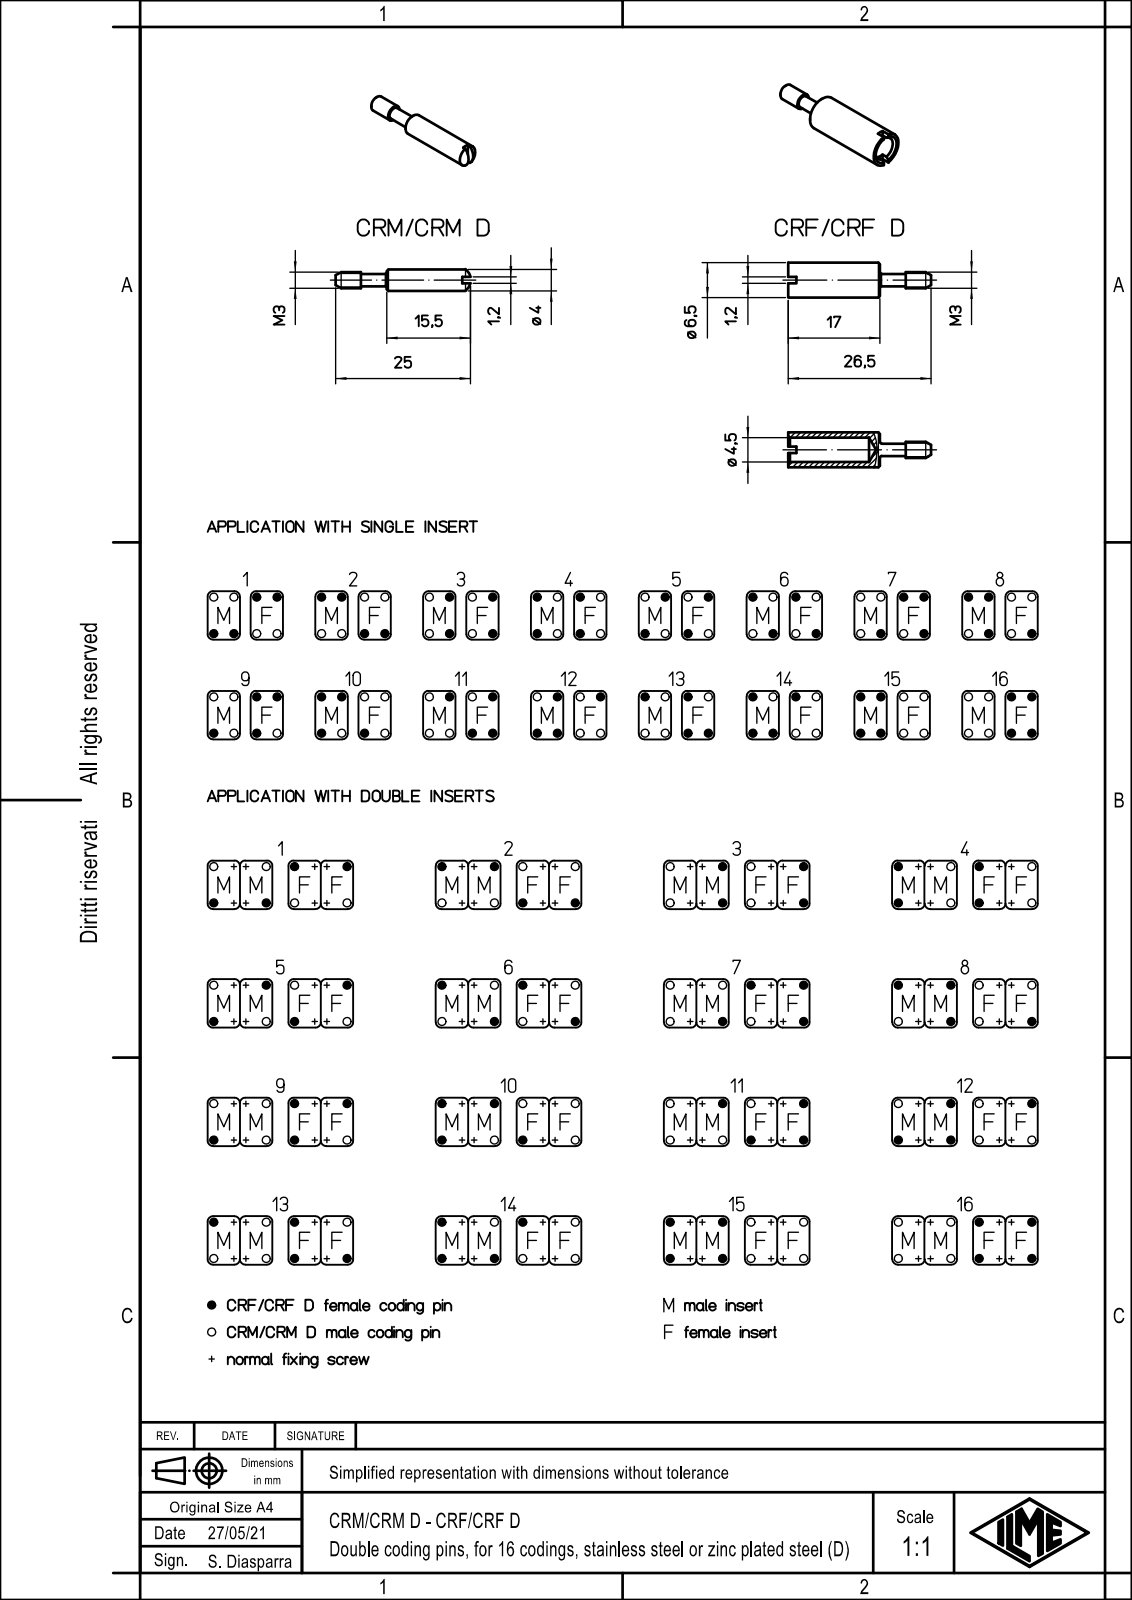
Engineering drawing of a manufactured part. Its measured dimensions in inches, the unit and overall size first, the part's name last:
Units: inches
Overall size (bounding box): 1.024 × 0.256 × 0.256
Round holes (diameter × count): ⌀0.177 ×1
Round bosses / shafts (diameter × count): ⌀0.256 ×1, ⌀0.118 ×1, ⌀0.098 ×1
Main face-to-face distances: 0.157, 0.512, 0.669, 0.354, 1.024, 0.031, 0.945, 0.591, 0.433, 0.079
Volume: 0.025 in³ · Surface area: 1.04 in²
Bodies: 1 solid, 27 faces (11 planar, 8 cylindrical, 8 other)
Part name (STEP PRODUCT): CRF D
STEP written by: Autodesk Inventor 7 (AUTOMOTIVE_DESIGN)
